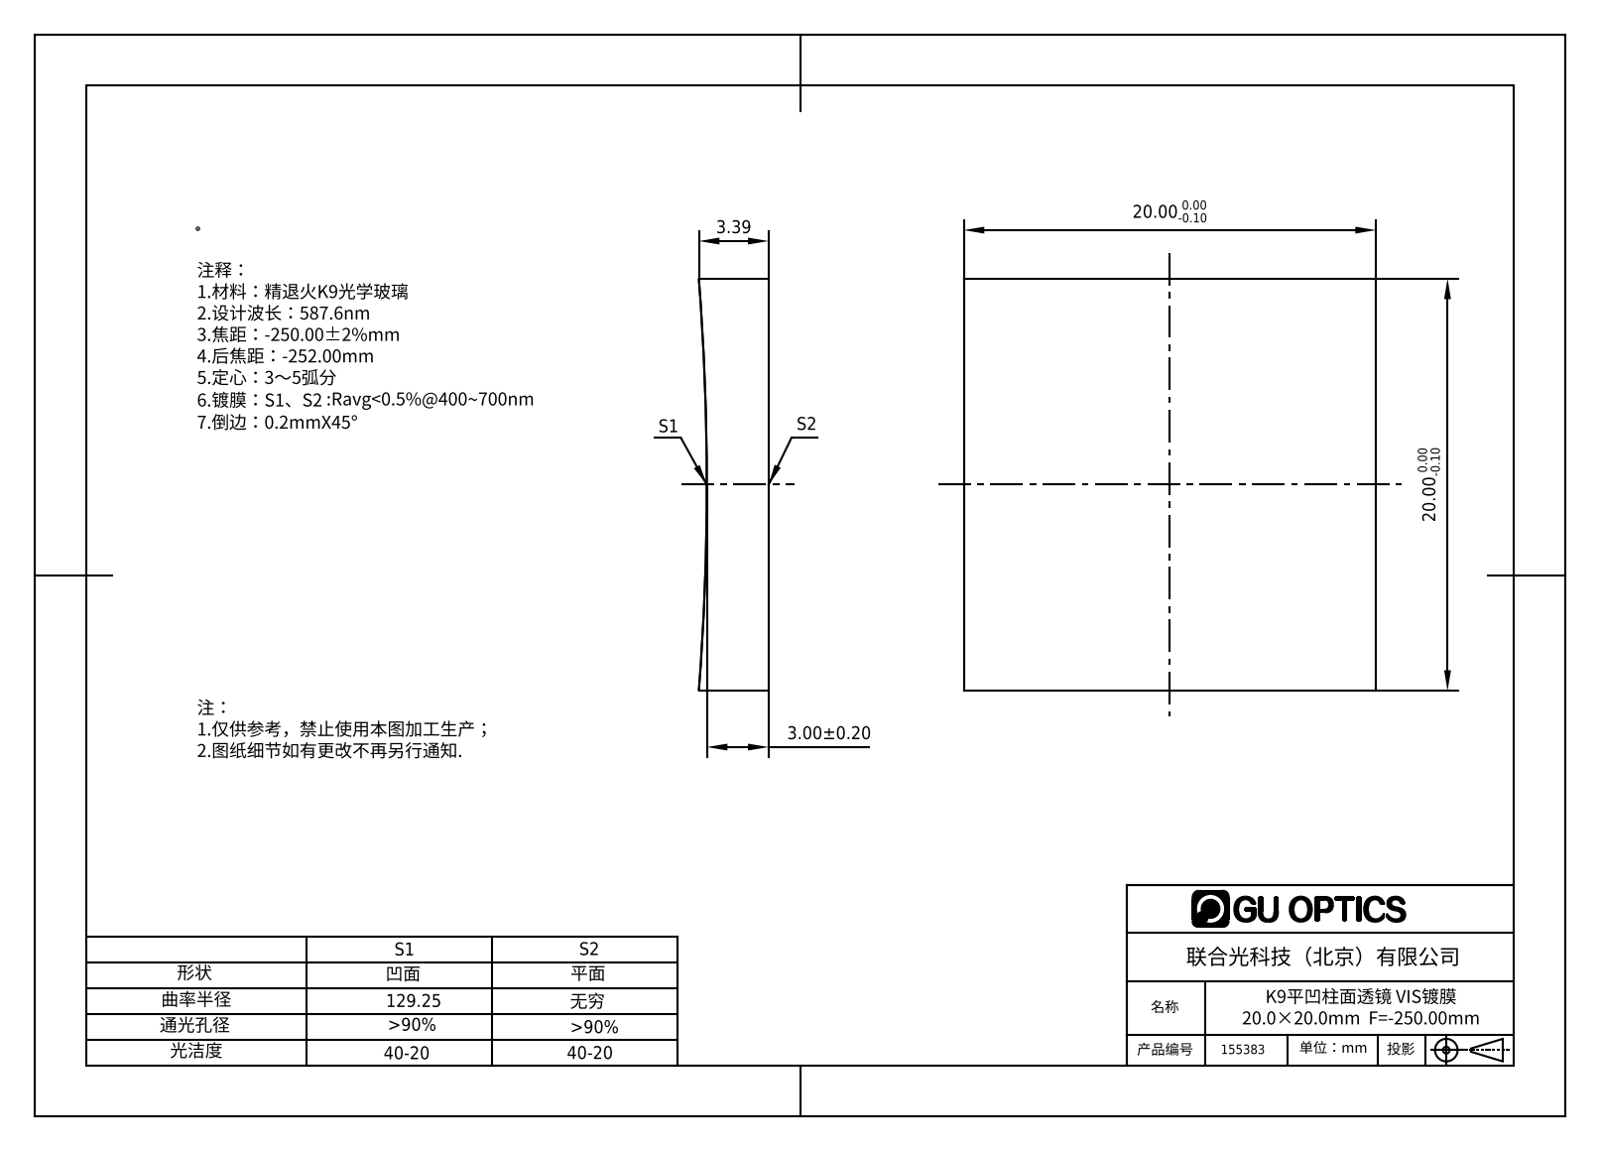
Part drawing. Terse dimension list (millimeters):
name: 155350
written by: SolidWorks 2016 (AUTOMOTIVE_DESIGN)
unit: mm
bodies: 1 solid, 6 faces (5 planar, 1 cylindrical, 0 other)
size: 20 × 20 × 3.39
volume: 1 252 mm³; area: 1 061 mm²
rounds: 1× R129.25
face distances: 20
